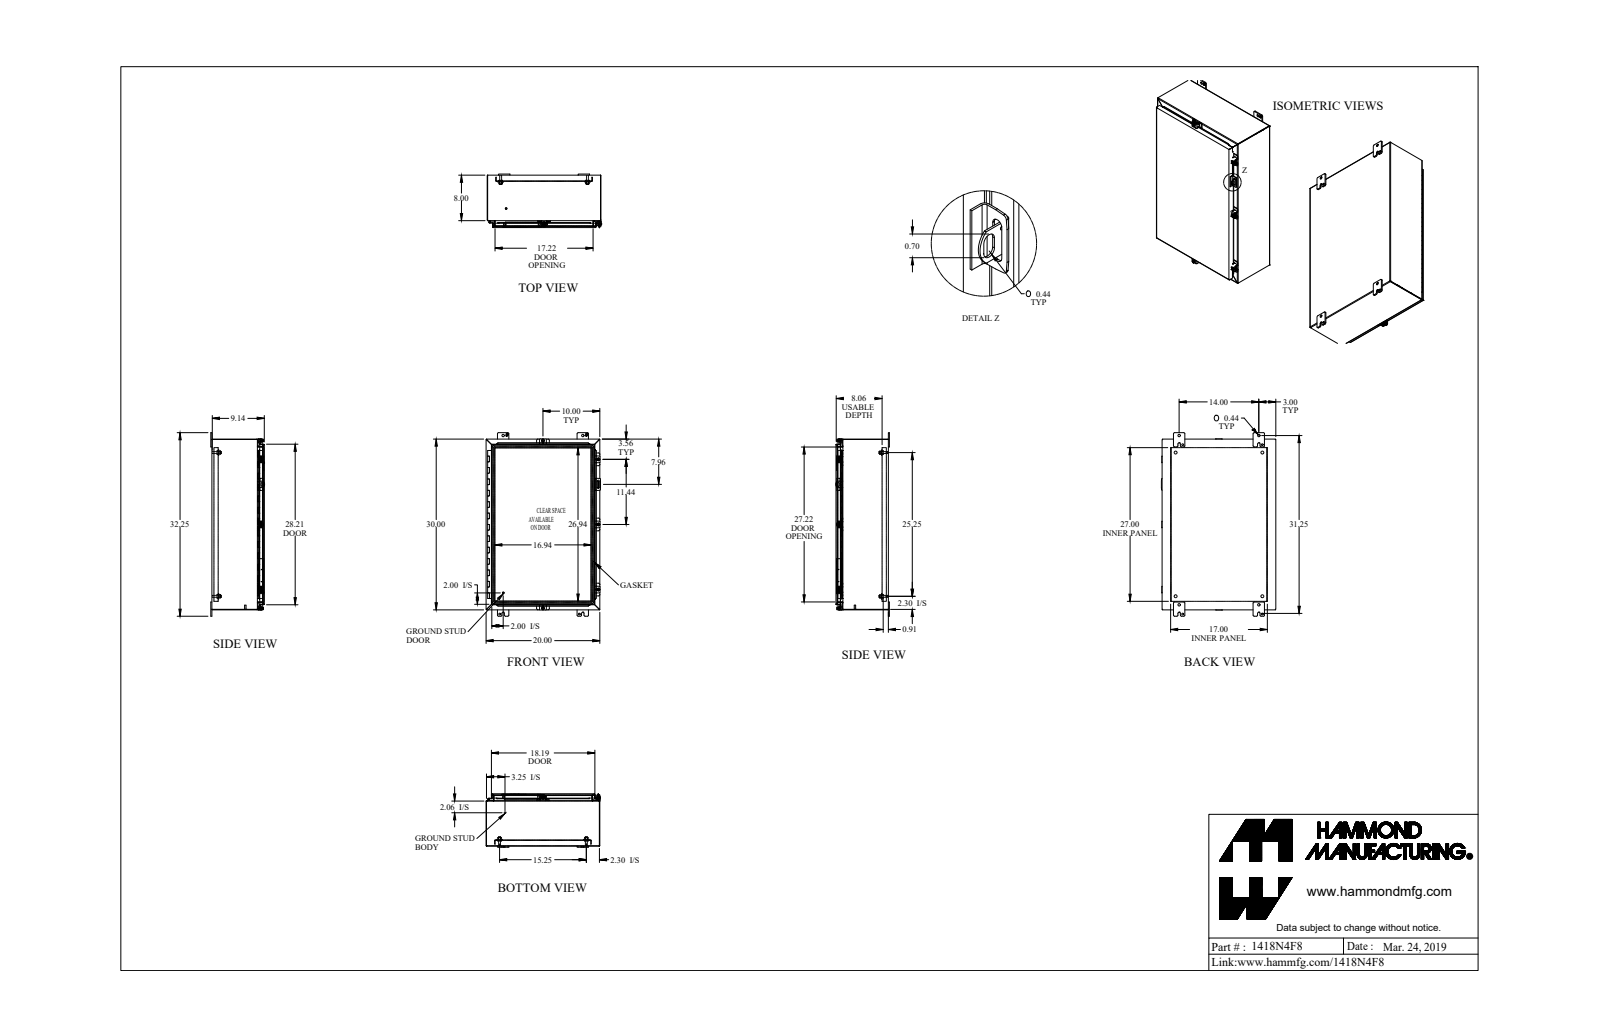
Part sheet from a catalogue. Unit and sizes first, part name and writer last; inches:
Units: inches
Overall size (bounding box): 32.25 × 20.126 × 9.437
Round holes (diameter × count): ⌀0.213 ×5, ⌀0.375 ×5, ⌀0.313 ×4, ⌀0.437 ×4, ⌀0.5 ×4, ⌀0.265 ×3, ⌀0.265 ×2, ⌀0.307 ×2, ⌀0.445 ×2, ⌀0.125 ×1, ⌀0.187 ×1
Round bosses / shafts (diameter × count): ⌀0.5 ×5, ⌀0.39 ×5, ⌀0.244 ×5, ⌀0.65 ×4, ⌀0.375 ×4, ⌀0.33 ×4, ⌀1 ×2, ⌀0.281 ×2
Partial cylindrical surfaces — rounded edges, fillets, slot ends (radius × count): R0.048 ×27, R0.143 ×27, R0.188 ×26, R0.036 ×24, R0.108 ×24, R0.25 ×24, R0.125 ×10, R0.141 ×10
Main face-to-face distances: 0.072, 0.072, 9.066, 9.138, 9.138, 9.21, 0.095, 19.928, 8.106, 8.034
Hole centre spacings: 29.498, 7.916, 28.417, 14, 21.478, 1.736, 2.434, 3.065
Volume: 225.1 in³ · Surface area: 5 895 in²
Bodies: 43 solids, 1601 faces (965 planar, 550 cylindrical, 86 other)
Part name (STEP PRODUCT): 1418N4F8_Default
STEP written by: SolidWorks 2019 (CONFIG_CONTROL_DESIGN)
